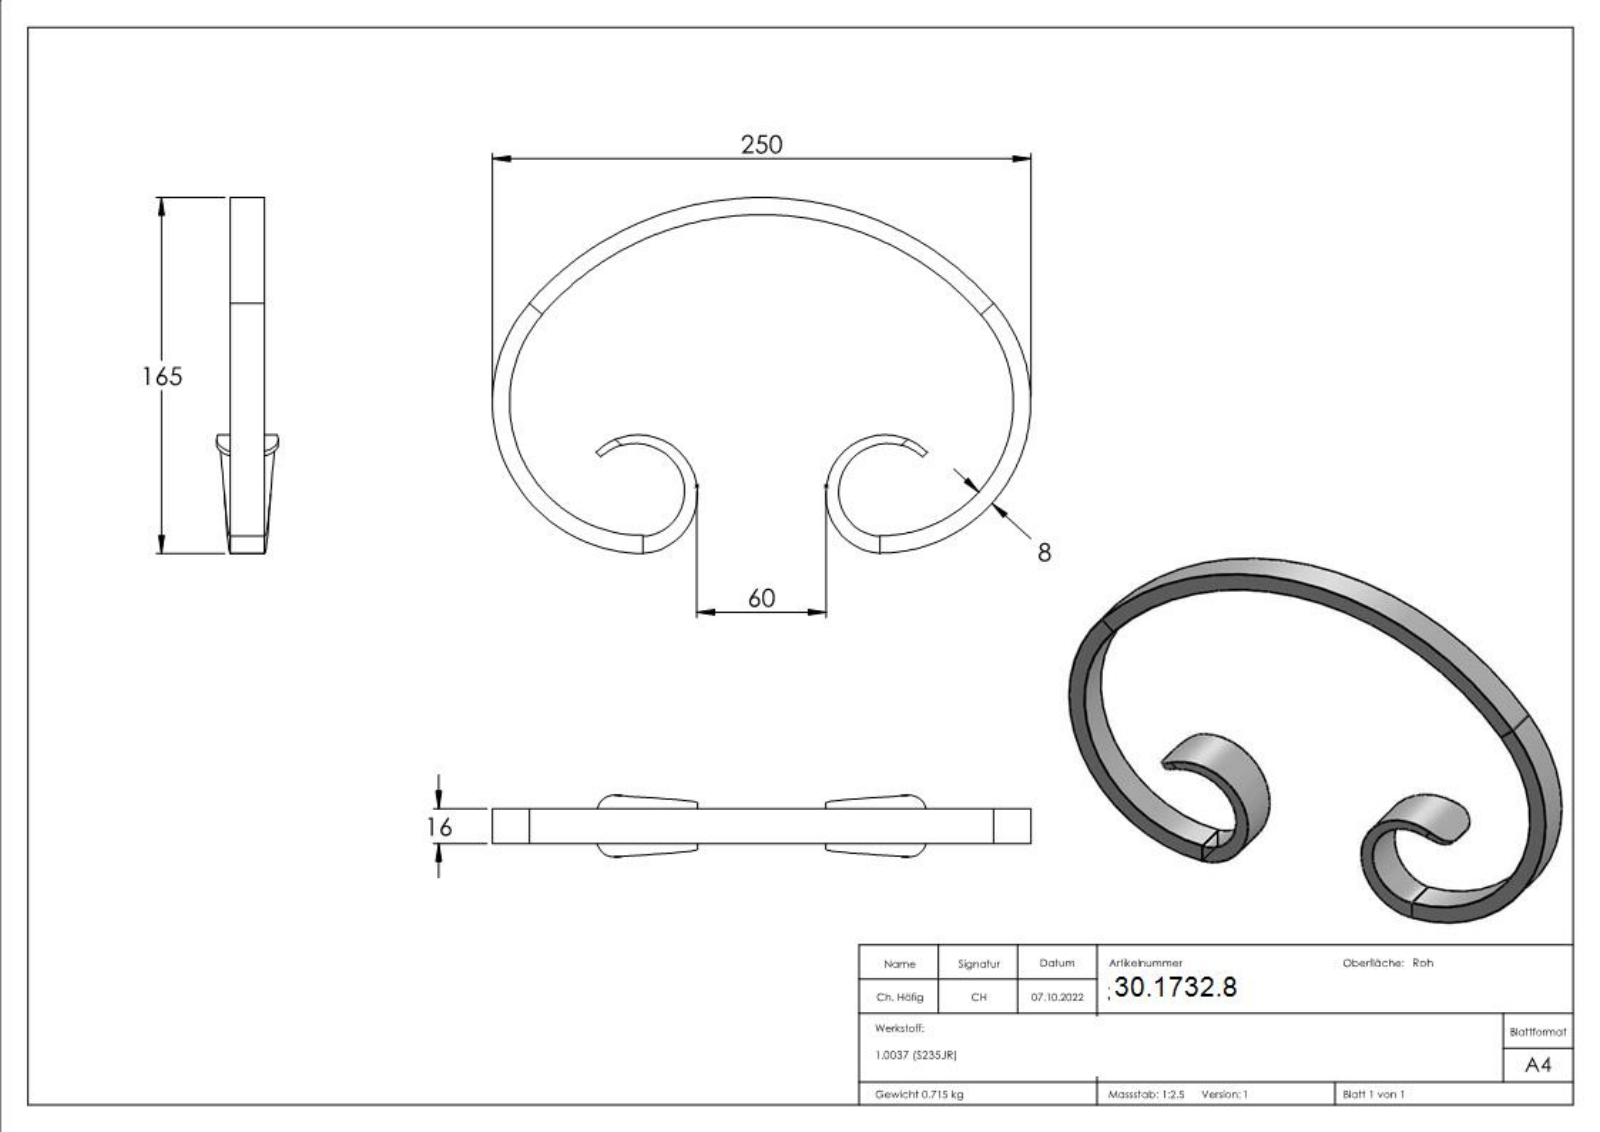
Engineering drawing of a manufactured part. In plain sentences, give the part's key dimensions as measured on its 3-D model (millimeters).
The part is named "3083". Its 3-D file was written by "SolidWorks 2018 (CONFIG_CONTROL_DESIGN)". It is 1 solid with 249 faces: 90 planar, 25 cylindrical and 134 other. Overall it measures 250 by 165 by 28.61 millimeters. Its volume is 91 625 cubic millimeters and its surface area 36 718 square millimeters. Partial cylindrical surfaces (rounded edges, fillets, slot ends): 2 of radius 62, 2 of radius 70, 1 of radius 135, 1 of radius 135.1, 1 of radius 143. The main face-to-face distances are 16, 3.15, 0.34, 0.39, 8, 1.84, 0.32, 2.97, 1.37, 0.58.
